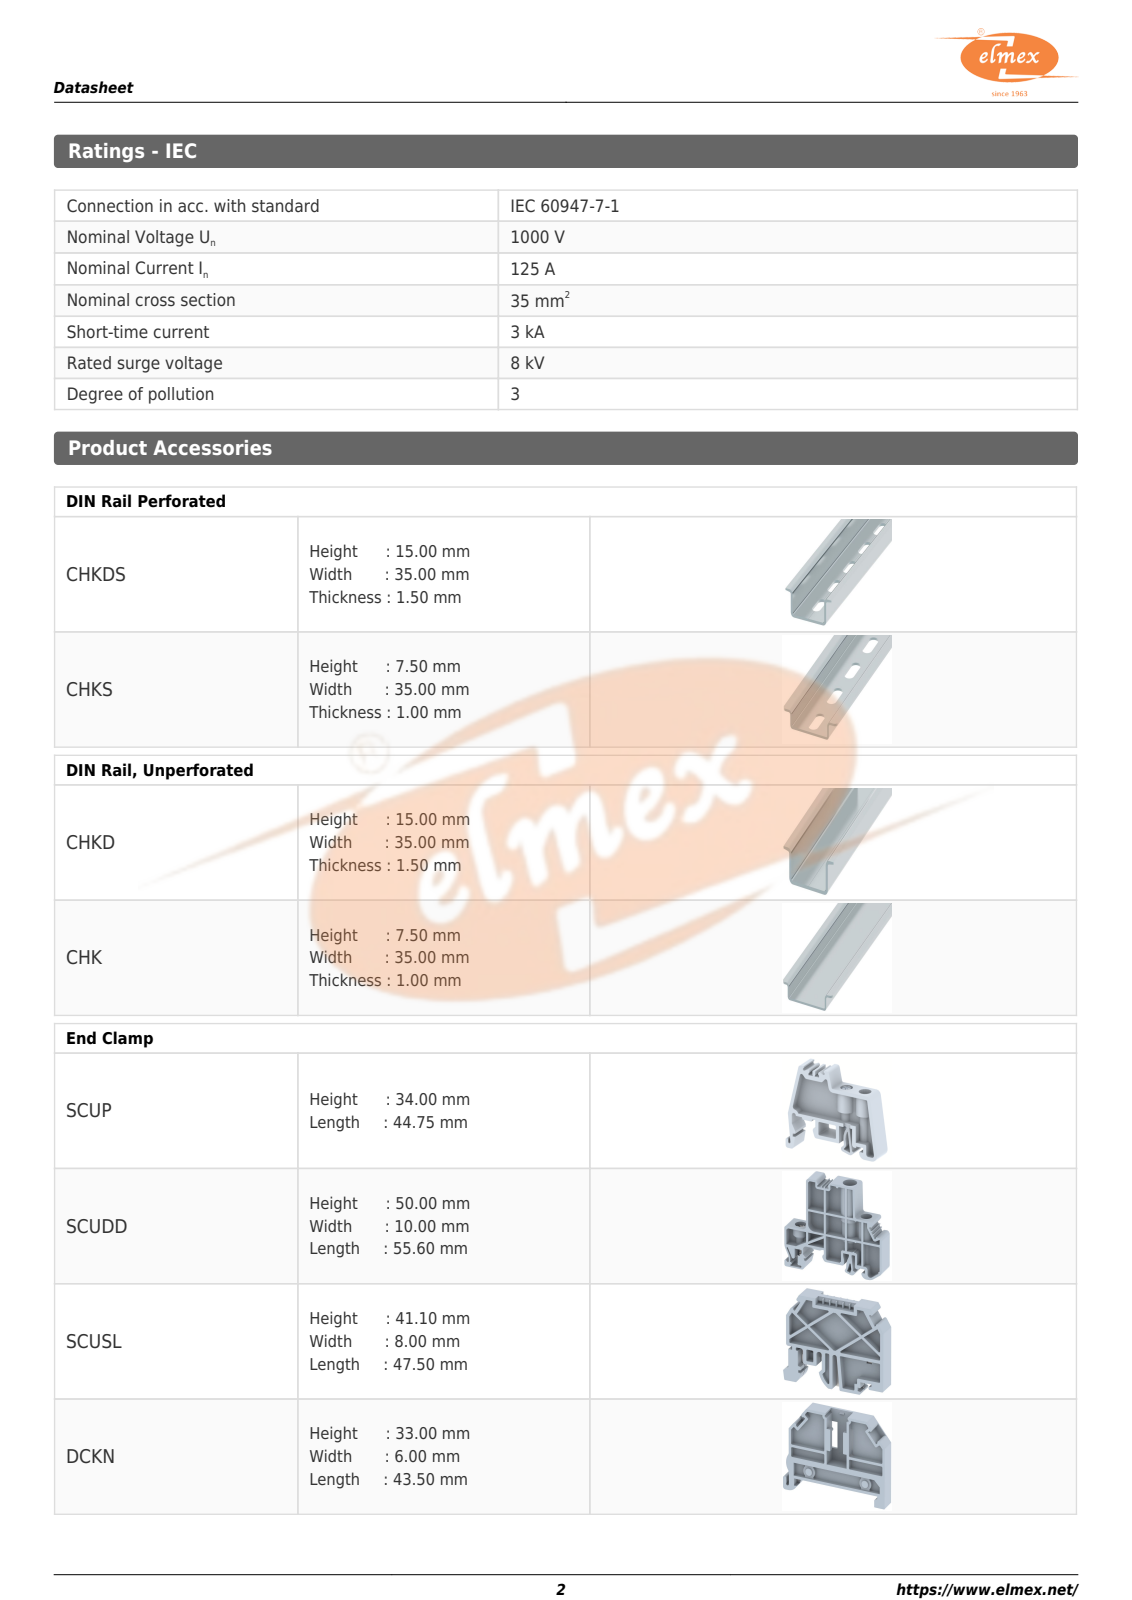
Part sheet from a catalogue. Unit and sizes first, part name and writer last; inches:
Units: inches
Overall size (bounding box): 3.937 × 2.382 × 0.63
Round holes (diameter × count): ⌀0.118 ×2
Partial cylindrical surfaces — rounded edges, fillets, slot ends (radius × count): R0.02 ×33, R0.008 ×9, R0.039 ×8, R0.01 ×5, R0.026 ×4, R0.197 ×3, R0.048 ×2, R0.079 ×2
Main face-to-face distances: 0.583, 0.039, 0.059, 0.047, 0.63, 0.217, 0.447, 0.291, 0.28, 0.232
Hole centre spacings: 3.565
Volume: 3.767 in³ · Surface area: 35.39 in²
Bodies: 1 solid, 359 faces (265 planar, 94 cylindrical, 0 other)
Part name (STEP PRODUCT): 6DST35H
STEP written by: ST-DEVELOPER v16 (AUTOMOTIVE_DESIGN)
